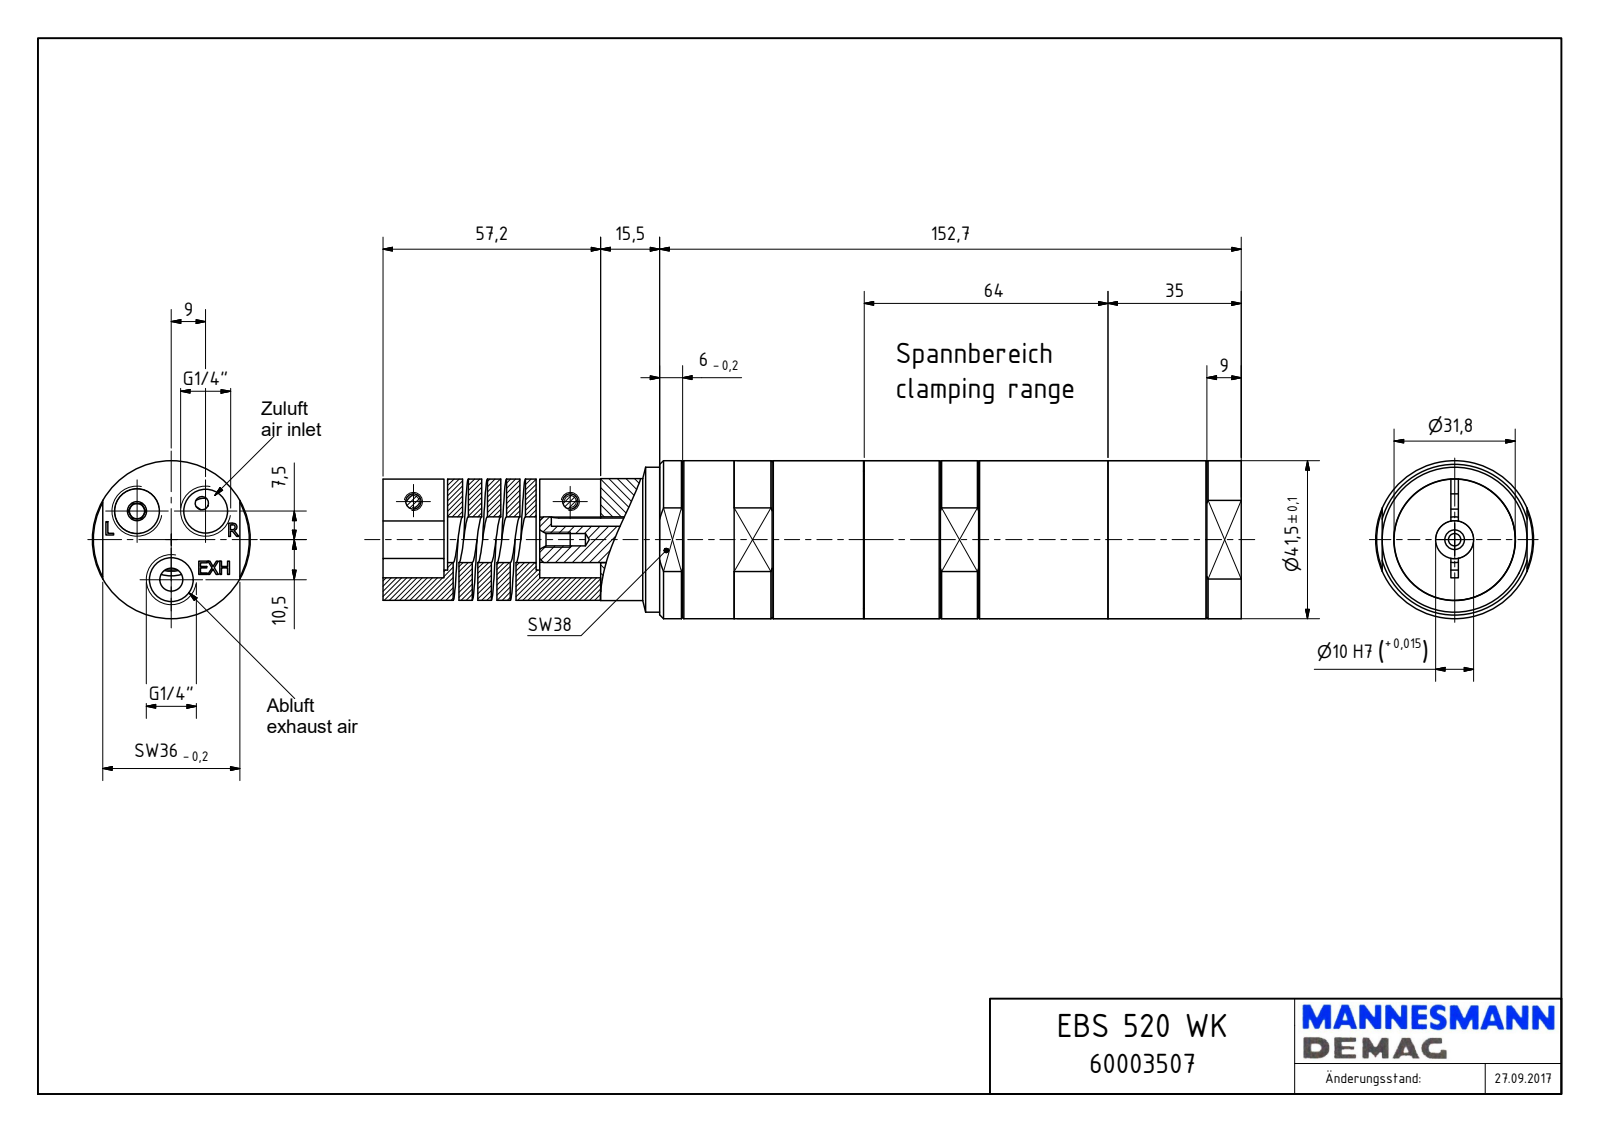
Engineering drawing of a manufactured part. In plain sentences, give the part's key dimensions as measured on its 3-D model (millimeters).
The part is named "EBS 520 WK_60003507". Its 3-D file was written by "Autodesk Inventor 2018 (AUTOMOTIVE_DESIGN)". It is 3 solids with 284 faces: 162 planar, 70 cylindrical and 52 other. Overall it measures 225.4 by 41.5 by 41.5 millimeters. Its volume is 250 660 cubic millimeters and its surface area 42 180 square millimeters. Round holes: 3 of diameter 4, 3 of diameter 11.45, 2 of diameter 8, 1 of diameter 3.24, 1 of diameter 10, 1 of diameter 12. Round bosses or shafts: 2 of diameter 7, 1 of diameter 41.5, 1 of diameter 38, 1 of diameter 36, 1 of diameter 32, 1 of diameter 31.8. Partial cylindrical surfaces (rounded edges, fillets, slot ends): 2 of radius 2. The main face-to-face distances are 1, 24.2, 17, 20, 18, 225.4, 16, 41.2, 184.2, 40.2. The hole center spacings are 11.72, 20.12, 10.5, 18, 41.2.
